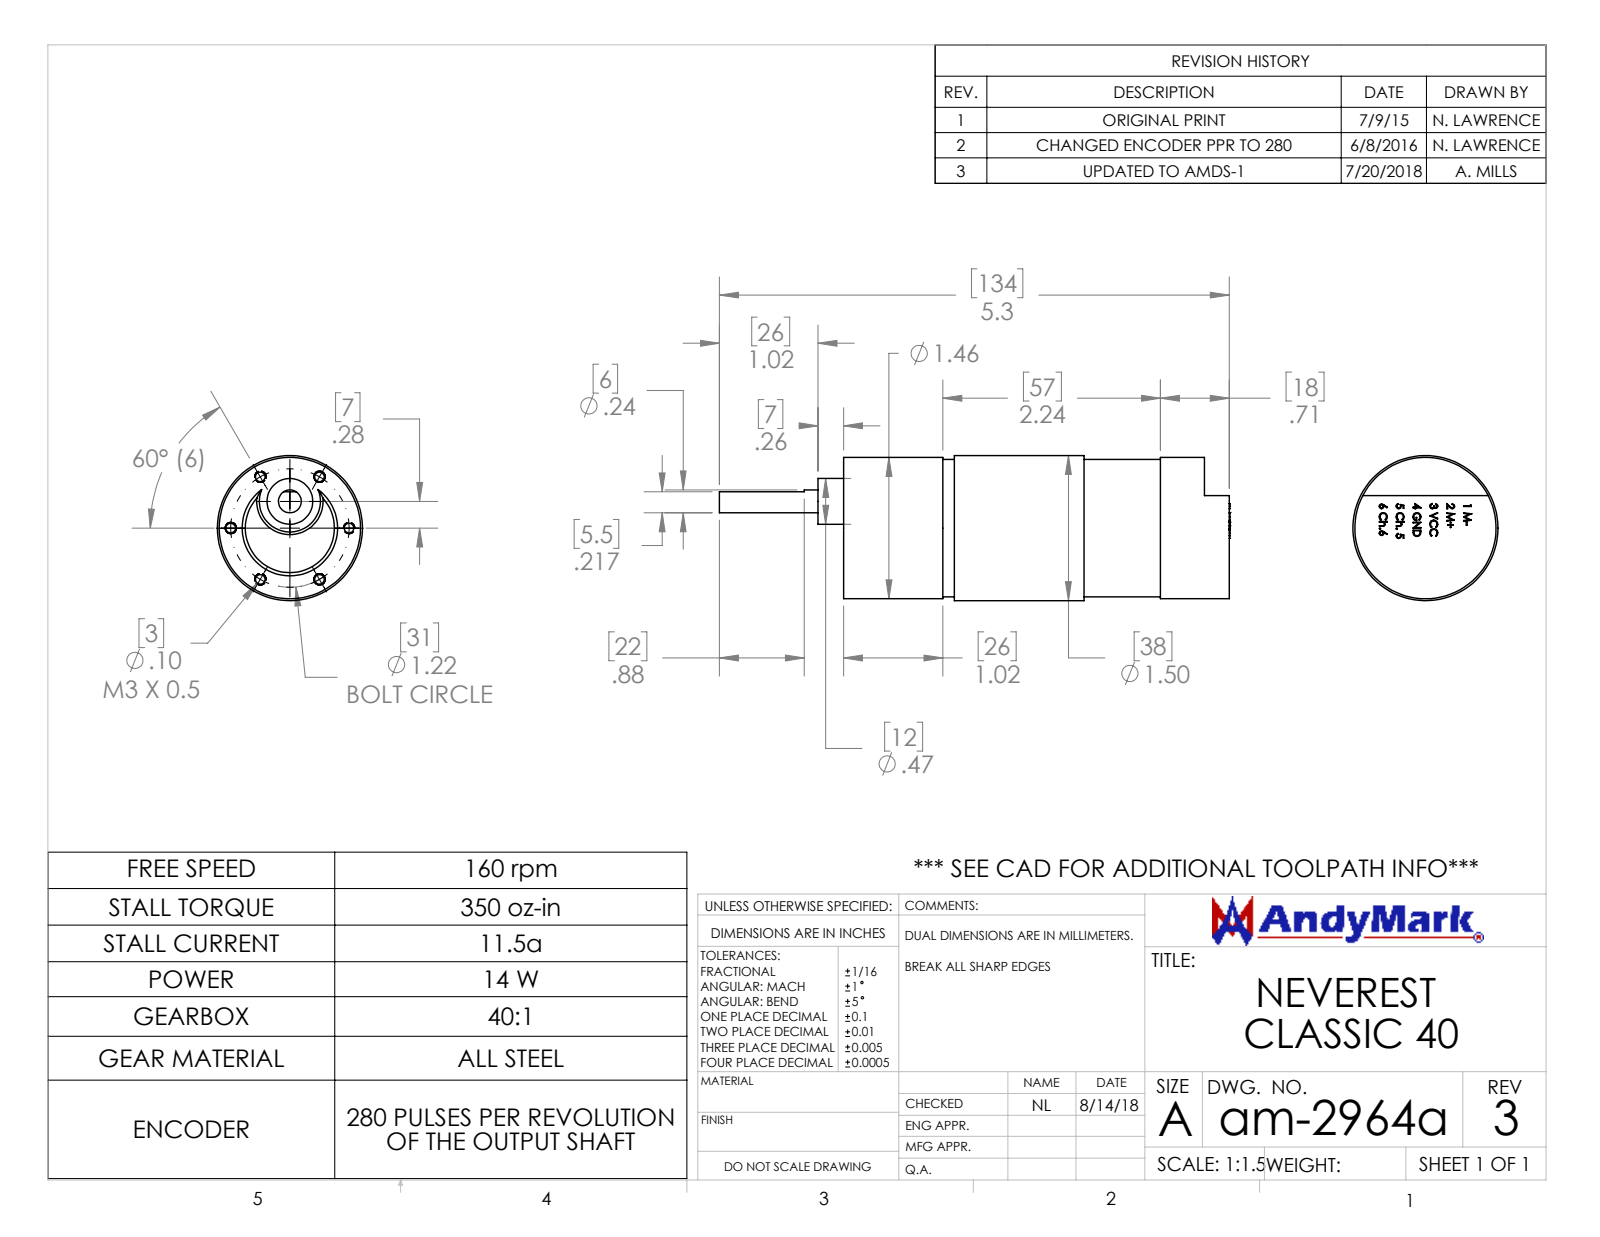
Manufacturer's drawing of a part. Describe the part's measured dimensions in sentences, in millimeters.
The part is named "am-2964a NeverRest Classic 40". Its 3-D file was written by "SolidWorks 2021 (AUTOMOTIVE_DESIGN)". It is 1 solid with 344 faces: 186 planar, 26 cylindrical and 132 other. Overall it measures 133.72 by 38 by 38 millimeters. Its volume is 108 922 cubic millimeters and its surface area 15 188 square millimeters. Round holes: 6 of diameter 2.5. Round bosses or shafts: 1 of diameter 38, 1 of diameter 37, 1 of diameter 36, 1 of diameter 12, 1 of diameter 6. The main face-to-face distances are 101, 0.7, 100.3, 6.5, 93.8, 94.5, 38, 72, 31.5, 65.5. The hole center spacings are 15.5, 26.85, 26.84, 30.99, 31.
